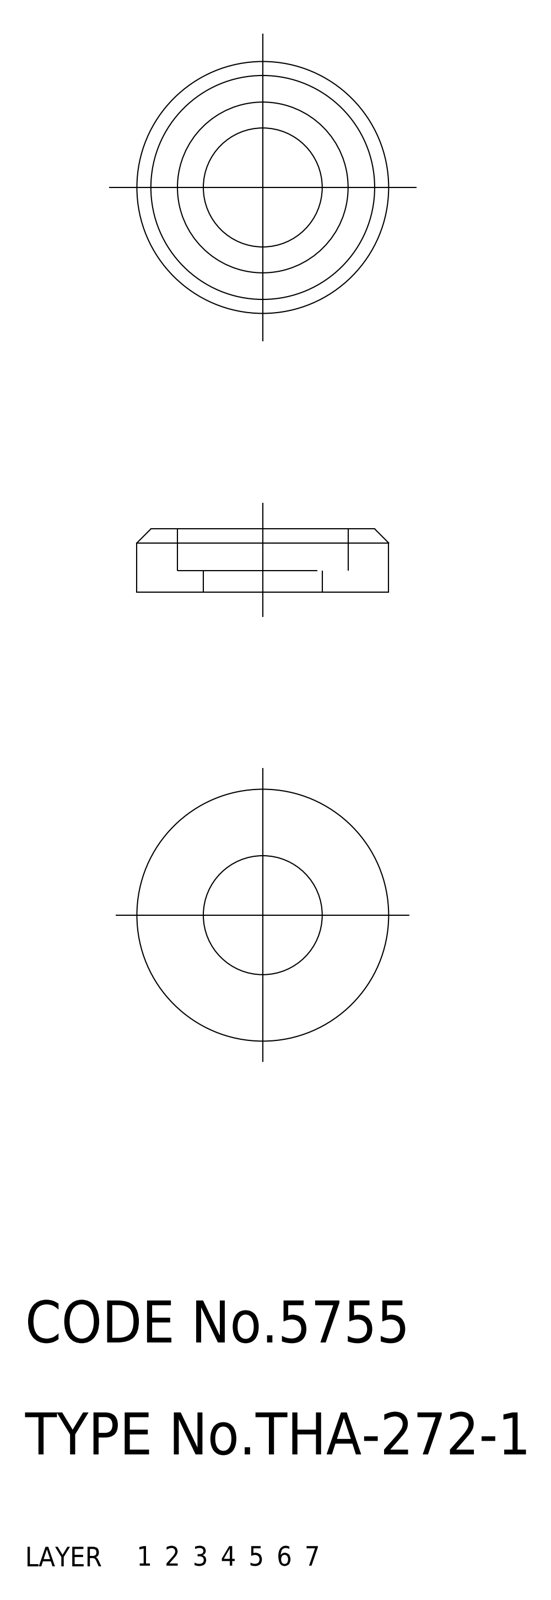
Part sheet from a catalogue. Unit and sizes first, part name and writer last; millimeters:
Units: millimetres
Overall size (bounding box): 18 × 18 × 4.5
Volume: 682 mm³ · Surface area: 771 mm²
Bodies: 1 solid, 11 faces (0 planar, 0 cylindrical, 11 other)
Part name (STEP PRODUCT): facing ring
STEP written by: CADfix (AUTOMOTIVE_DESIGN)
